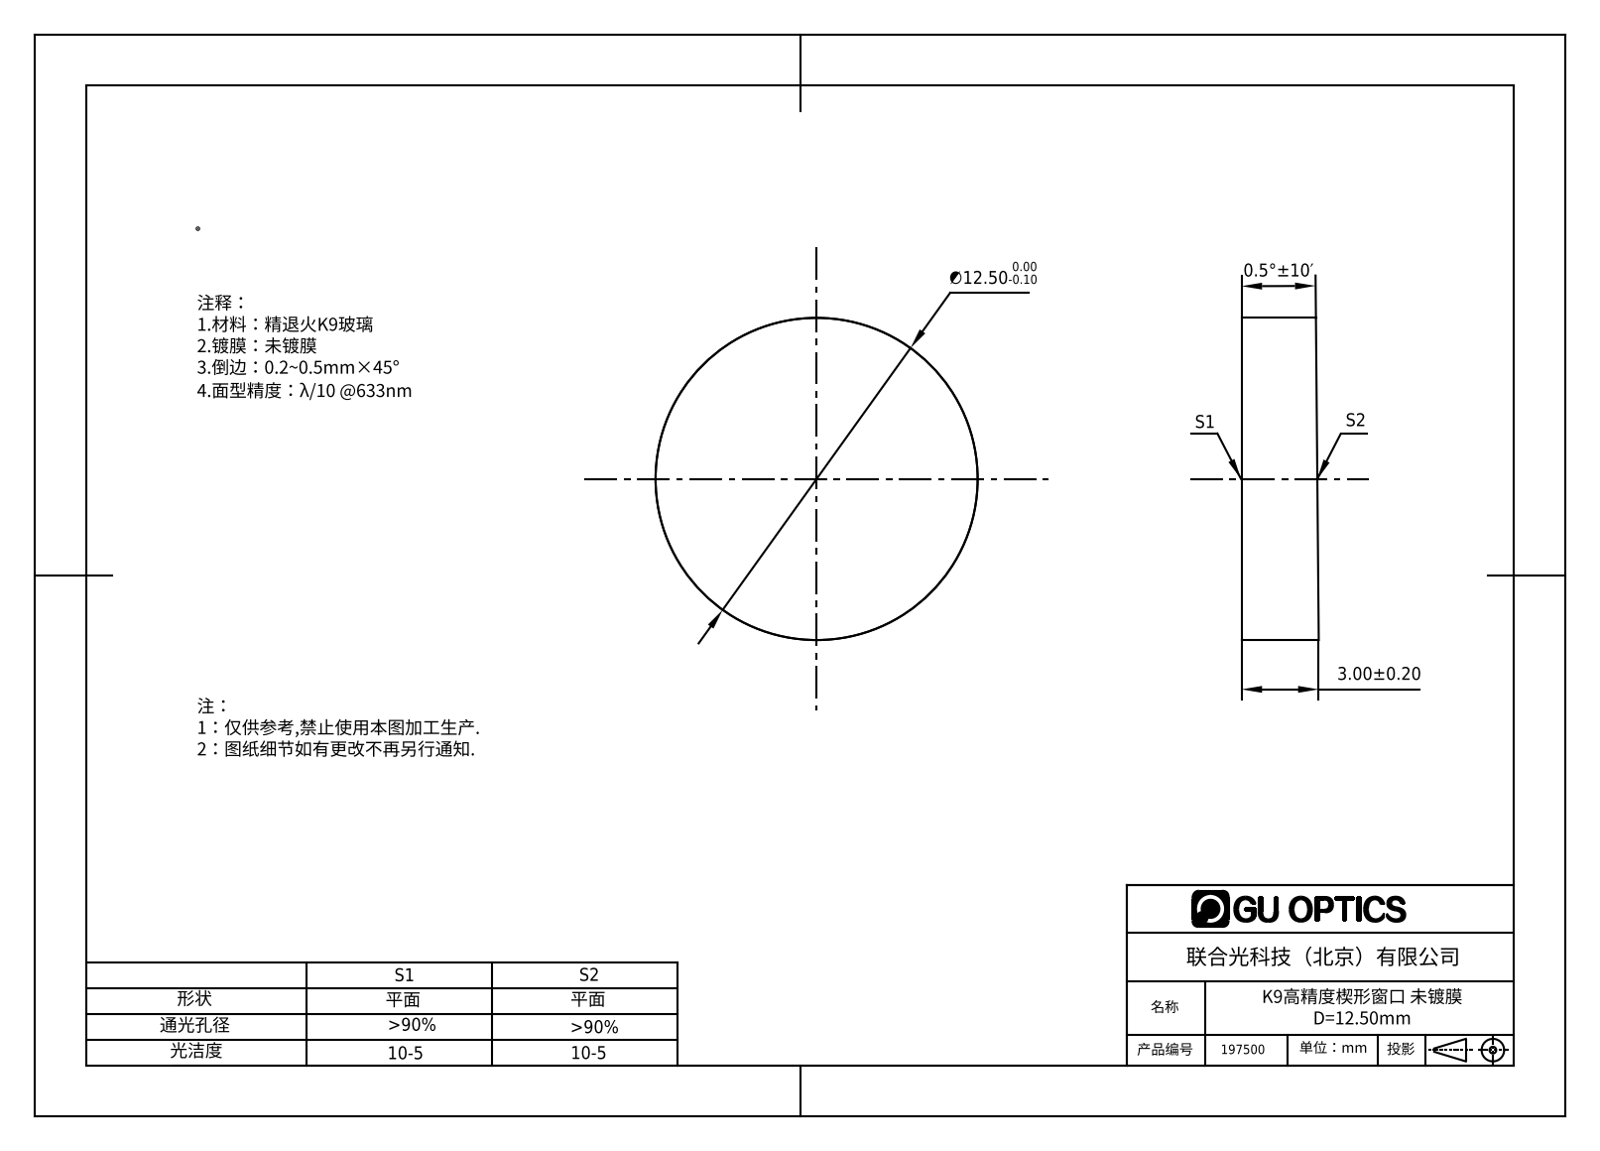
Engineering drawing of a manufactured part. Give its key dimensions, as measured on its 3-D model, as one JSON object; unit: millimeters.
{"part_name": "197500", "step_written_by": "SolidWorks 2016 (AUTOMOTIVE_DESIGN)", "units": "millimeters", "bodies": {"solids": 1, "faces": 4, "planar": 2, "cylindrical": 2, "other": 0}, "overall_size": [12.5, 12.5, 3], "volume_mm3": 361, "surface_area_mm2": 361, "round_bosses_or_shafts": [[12.5, 1]]}
